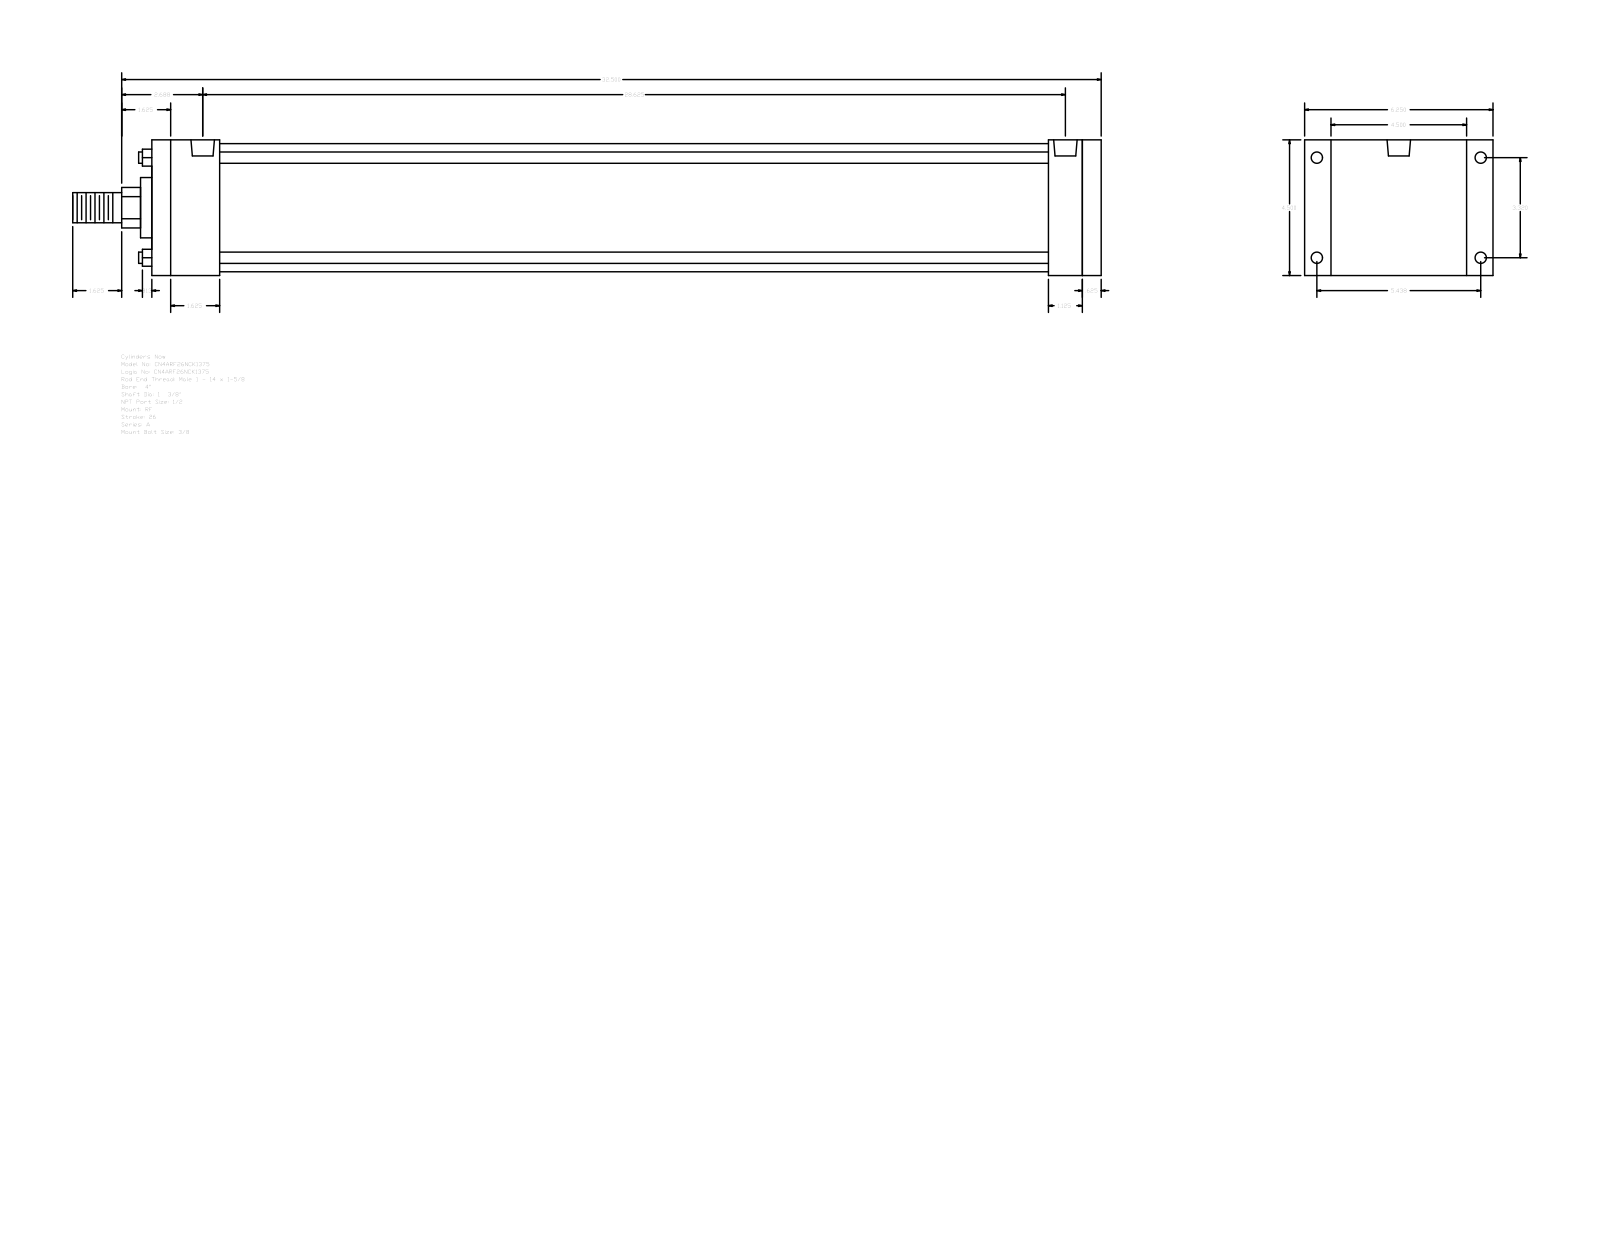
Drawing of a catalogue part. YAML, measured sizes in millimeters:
part_name: "A_RF__0400_1.375"
step_written_by: "GSSL Pune (CONFIG_CONTROL_DESIGN)"
units: millimeters
bodies: {solids: 0, faces: 92, planar: 64, cylindrical: 28, other: 0}
overall_size: [866.77, 158.75, 114.3]
round_holes:
  - {diameter: 8.73, count: 4}
  - {diameter: 9.53, count: 4}
  - {diameter: 19.77, count: 2}
round_bosses_or_shafts:
  - {diameter: 9.53, count: 4}
  - {diameter: 107.95, count: 1}
  - {diameter: 50.8, count: 1}
  - {diameter: 34.92, count: 1}
  - {diameter: 25.4, count: 1}
partial_cylinders:
  - {radius: 17.06, count: 1}
face_to_face_distances: [114.3, 800.1, 15.88, 784.22, 57.15, 22.23, 136.53, 755.65, 28.57, 44.45]
hole_center_spacings: [3.18, 84.32, 138.12, 161.82, 720.72, 723.9, 727.08]
